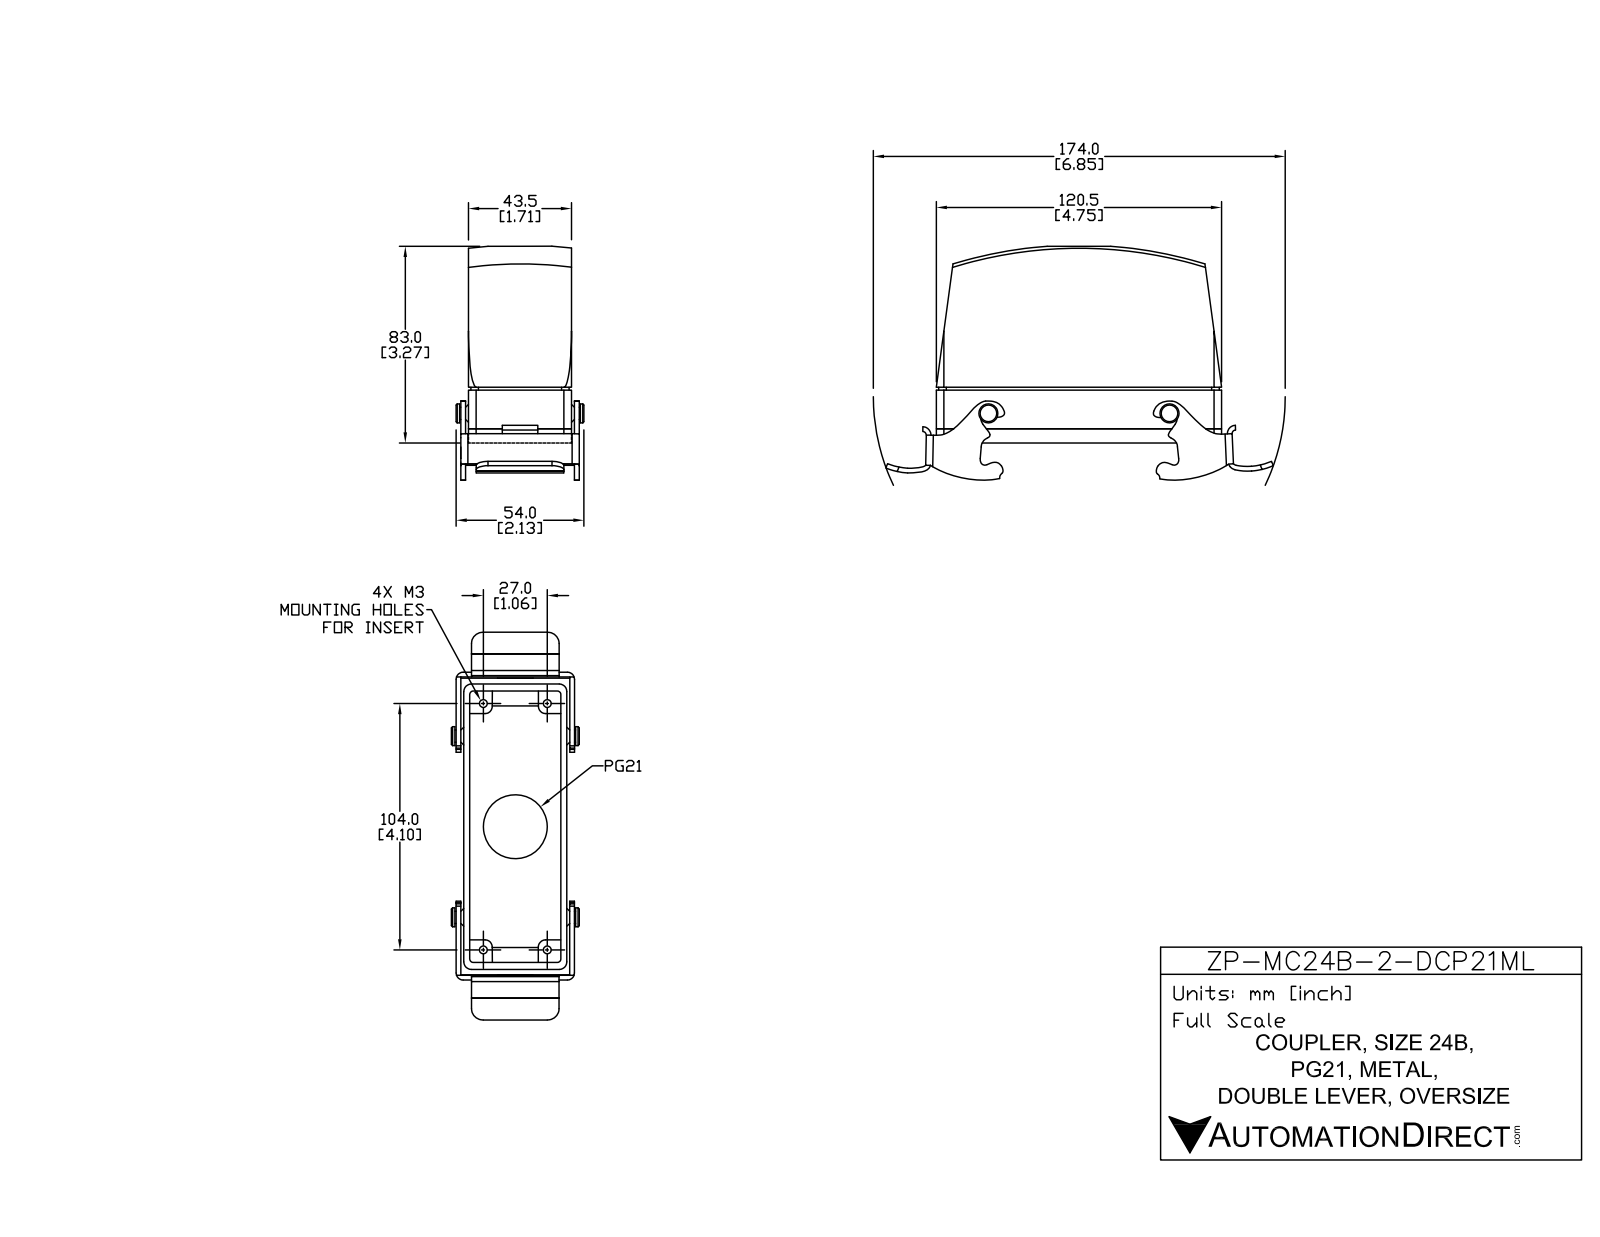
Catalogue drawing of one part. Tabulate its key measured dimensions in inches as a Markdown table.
| quantity | value |
| --- | --- |
| part name | ZP-MC24B-2-DCP21ML |
| STEP written by | SolidWorks 2011 (AUTOMOTIVE_DESIGN) |
| units | inches |
| bodies | 12 solids, 298 faces (142 planar, 142 cylindrical, 14 other) |
| overall size | 6.022 × 3.764 × 2.126 |
| volume | 5.439 in³ |
| surface area | 119.7 in² |
| round holes (diameter × count) | 0.138 × 4, 1.063 × 1 |
| round bosses / shafts (diameter × count) | 0.315 × 2, 0.204 × 2 |
| partial cylindrical surfaces (radius × count) | 0.039 × 12, 0.02 × 10, 0.126 × 8, 0.079 × 6, 0.118 × 6, 0.157 × 6, 0.03 × 4, 0.059 × 4 |
| main face-to-face distances | 0.098, 1.614, 1.713, 1.516, 0.039, 1.762, 0.049, 0.089, 0.148, 0.187 |
| hole center spacings | 2.115, 1.063, 4.094, 4.23 |
